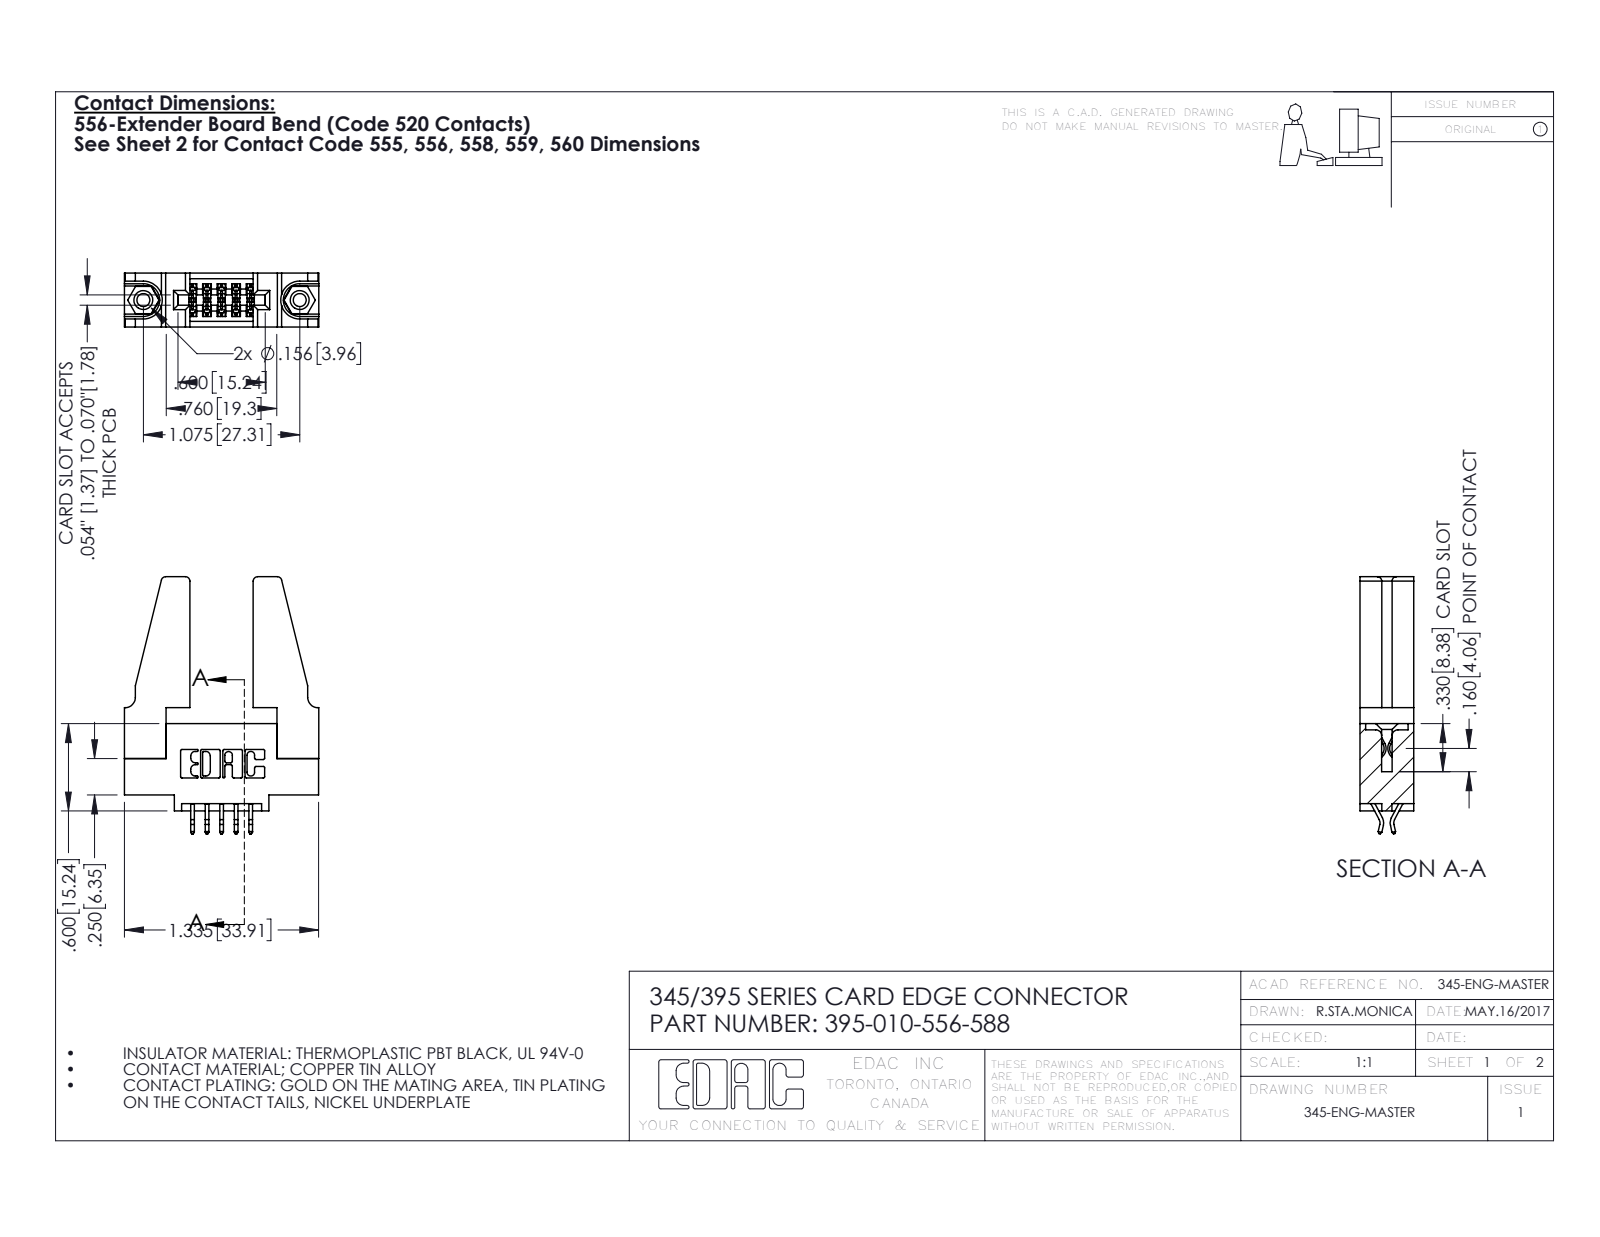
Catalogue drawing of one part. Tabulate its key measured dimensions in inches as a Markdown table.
| quantity | value |
| --- | --- |
| part name | 395-010-556-588; 345-220-078_345-220-088; 345-250-001_345-250-001-102; 345 Part_0.110 Offset - 0.156 Dia-TH (+1 more) |
| STEP written by | SolidWorks 2016 (CONFIG_CONTROL_DESIGN) |
| units | inches |
| bodies | 15 solids, 814 faces (526 planar, 272 cylindrical, 16 other) |
| overall size | 1.767 × 1.336 × 0.37 |
| volume | 0.374 in³ |
| surface area | 10.46 in² |
| round holes (diameter × count) | 0.089 × 2, 0.125 × 2, 0.156 × 2, 0.064 × 1 |
| round bosses / shafts (diameter × count) | 0.155 × 2 |
| partial cylindrical surfaces (radius × count) | 0.01 × 22, 0.006 × 15, 0.03 × 8, 0.007 × 6, 0.031 × 6, 0.026 × 3, 0.01 × 2, 0.014 × 2 |
| main face-to-face distances | 0.37, 0.072, 0.298, 0.2, 0.148, 0.15, 0.22, 0.077, 0.45, 0.225 |
| hole center spacings | 0.27, 0.847, 1.075 |
